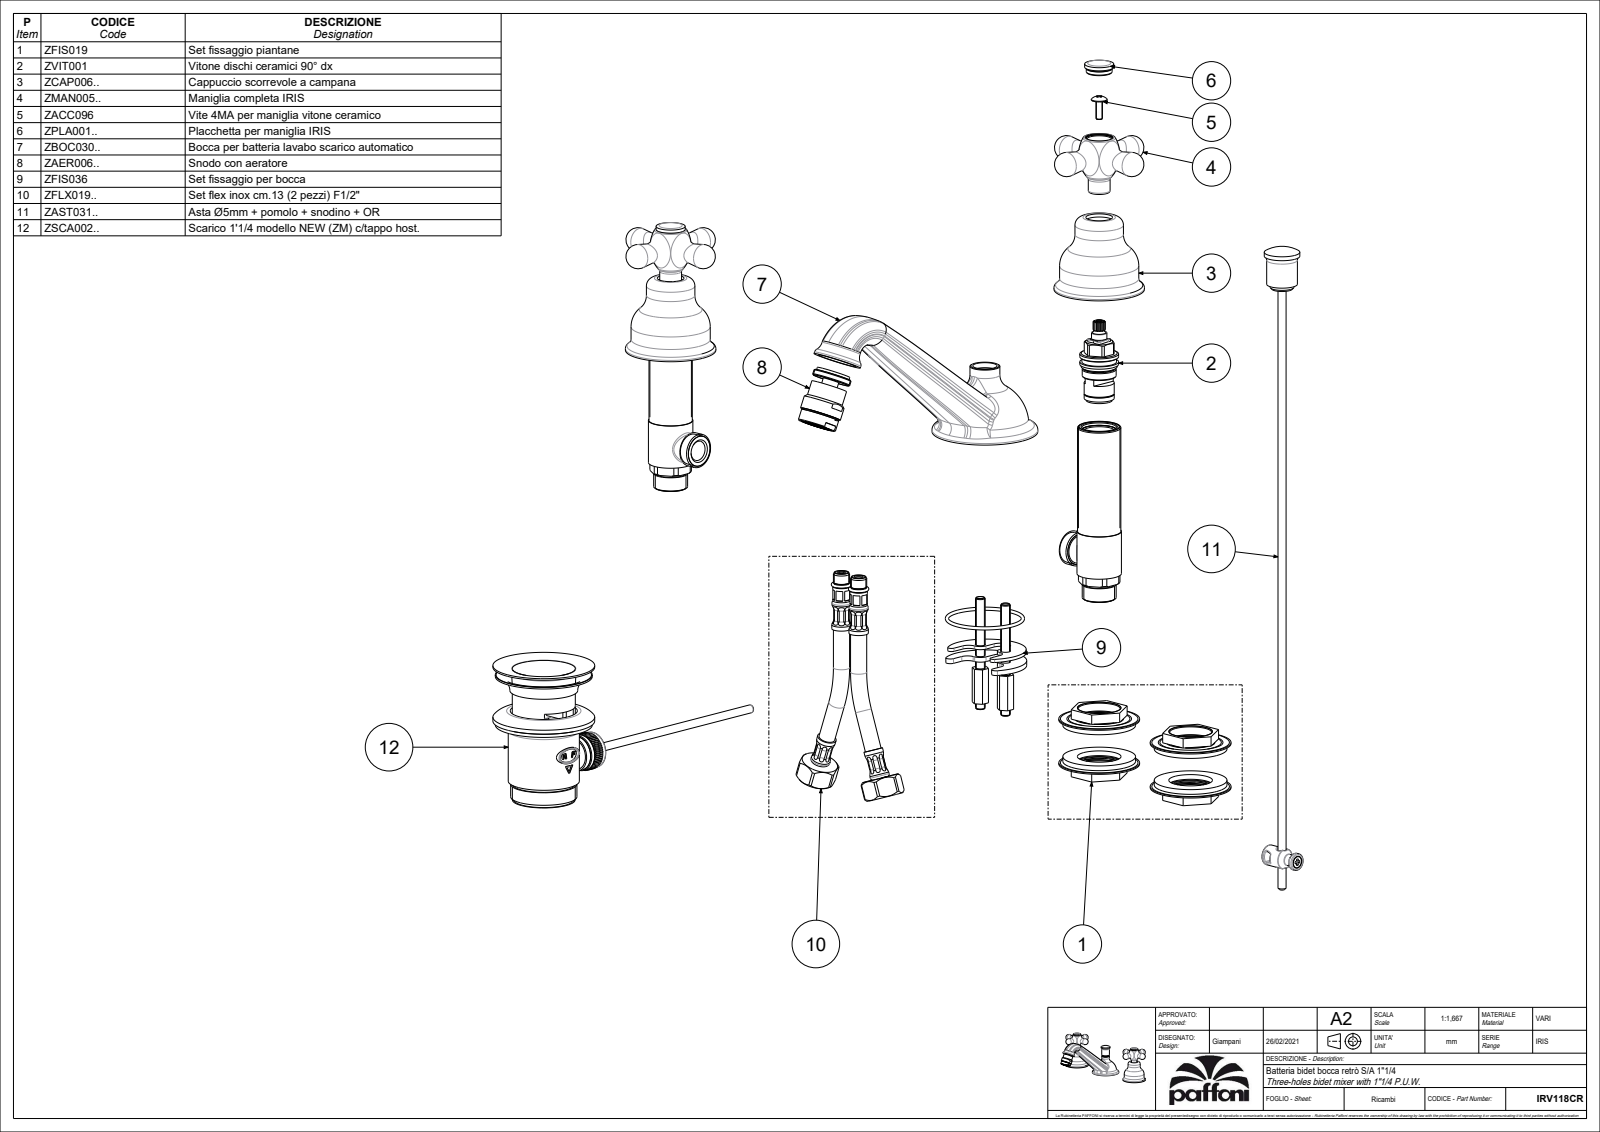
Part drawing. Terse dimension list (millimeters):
name: IRV118CR
written by: CREO PARAMETRIC BY PTC INC, 2020044 (CONFIG_CONTROL_DESIGN)
unit: mm
bodies: 3 solids, 277 faces (22 planar, 42 cylindrical, 213 other)
size: 272 × 188.09 × 94.3
volume: 329 750 mm³; area: 57 567 mm²
bosses: 2× ⌀55, 2× ⌀49, 2× ⌀28, 2× ⌀24, 2× ⌀18, 2× ⌀13.5, 1× ⌀65.5, 1× ⌀30
face distances: 3, 28.69, 25.69, 46.5, 42.8, 3.7, 45.8, 0.7, 7.69, 18
